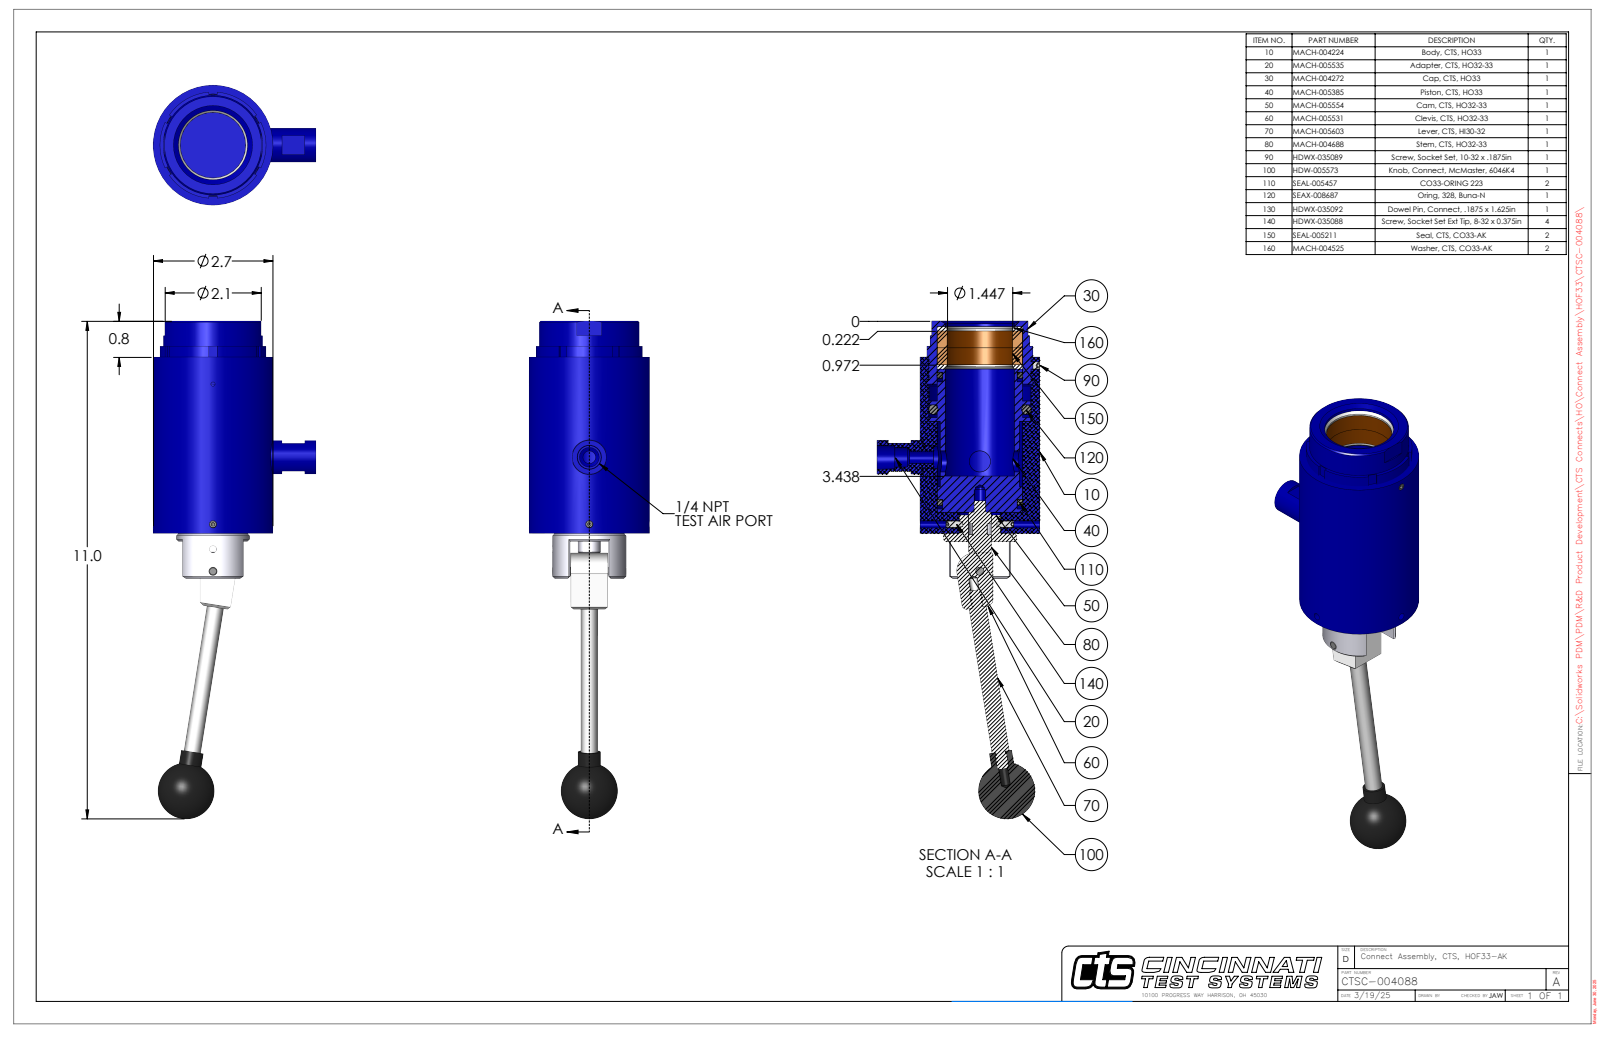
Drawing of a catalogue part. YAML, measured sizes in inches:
part_name: "CTSC-004088"
step_written_by: "SolidWorks 2023 (AUTOMOTIVE_DESIGN)"
units: inches
bodies: {solids: 15, faces: 546, planar: 179, cylindrical: 226, other: 141}
overall_size: [11.035, 3.6, 2.65]
volume: 21.49
surface_area: 134.4
round_holes:
  - {diameter: 0.201, count: 3}
  - {diameter: 0.159, count: 2}
  - {diameter: 0.469, count: 2}
  - {diameter: 0.094, count: 1}
  - {diameter: 0.189, count: 1}
  - {diameter: 0.19, count: 1}
  - {diameter: 0.25, count: 1}
  - {diameter: 0.281, count: 1}
  - {diameter: 0.438, count: 1}
  - {diameter: 0.5, count: 1}
  - {diameter: 0.516, count: 1}
  - {diameter: 0.542, count: 1}
round_bosses_or_shafts:
  - {diameter: 0.75, count: 2}
  - {diameter: 0.5, count: 2}
  - {diameter: 0.164, count: 2}
  - {diameter: 0.109, count: 2}
  - {diameter: 2.65, count: 1}
  - {diameter: 2.344, count: 1}
  - {diameter: 2.2, count: 1}
  - {diameter: 1.885, count: 1}
partial_cylinders:
  - {radius: 0.385, count: 1}
  - {radius: 0.4, count: 1}
  - {radius: 1.13, count: 1}
  - {radius: 1.208, count: 1}
face_to_face_distances: [0.844, 0.094, 0.75, 3.736, 4.486, 0.375, 0.375, 4.111, 0.469, 3.642]
hole_center_spacings: [0.093, 0.488, 1.713, 1.945, 2.033, 2.126, 2.433, 3.658]
